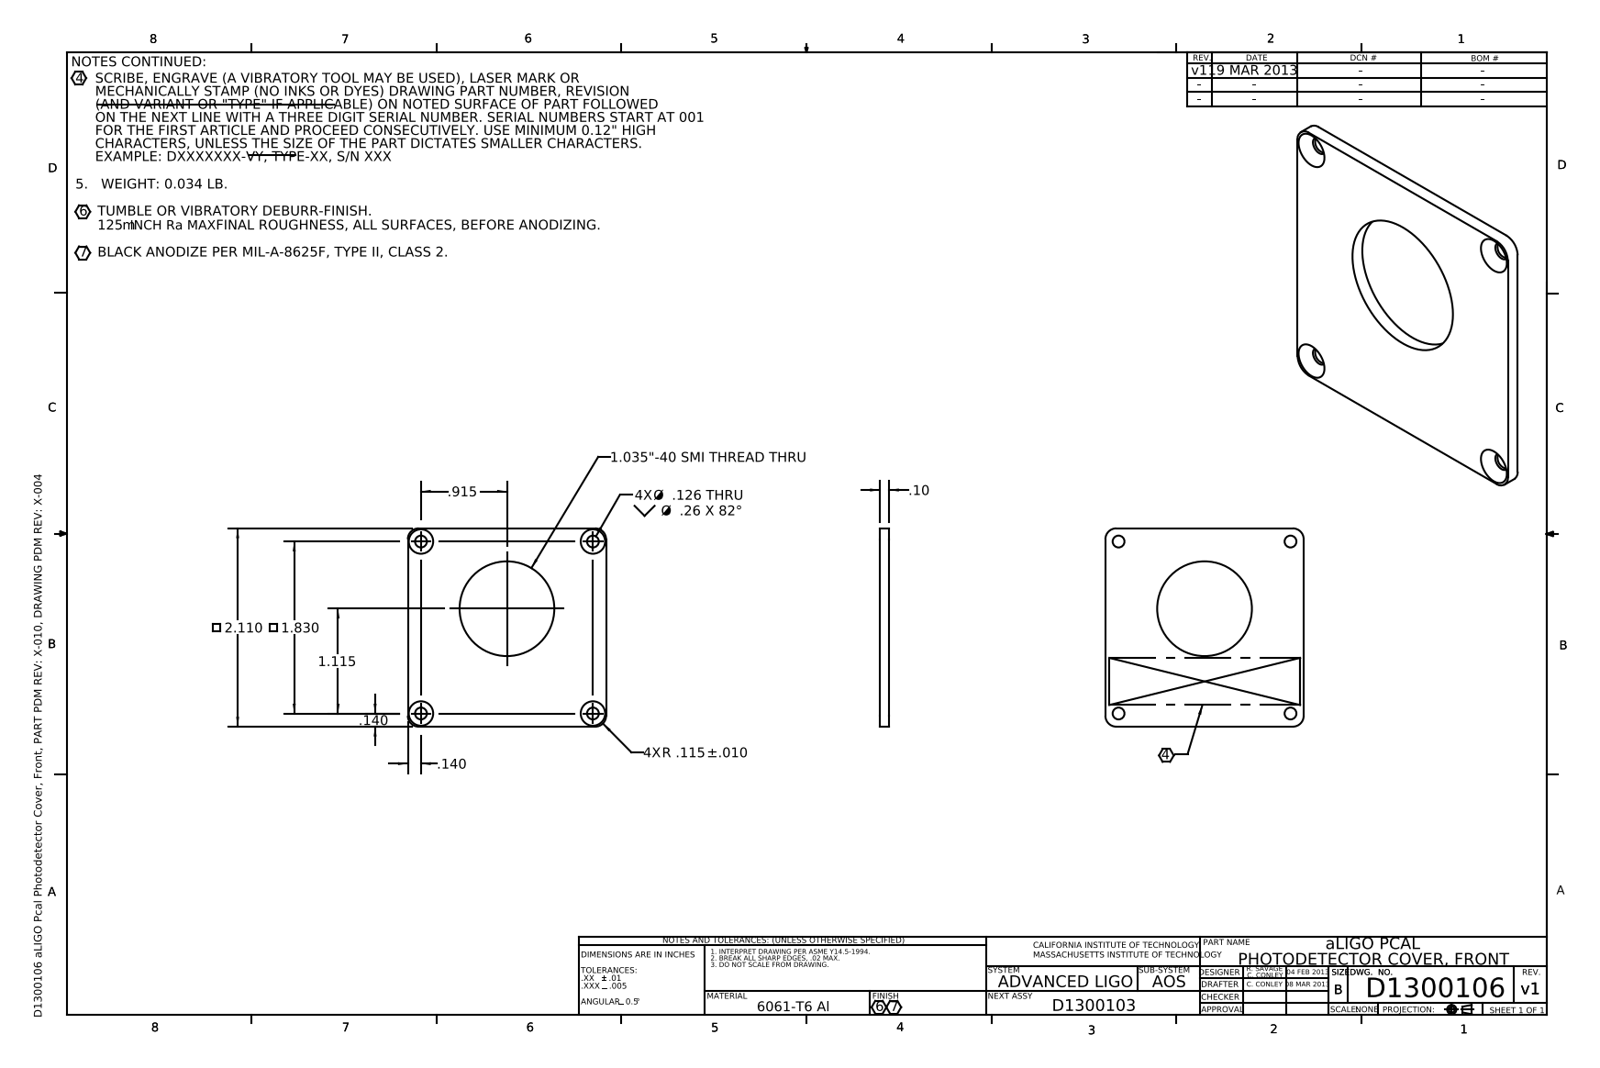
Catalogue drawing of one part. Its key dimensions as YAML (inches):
part_name: "D1300106-v1 aLIGO Pcal Photodetector Cover, Front"
step_written_by: "SolidWorks 2013 (AUTOMOTIVE_DESIGN)"
units: inches
bodies: {solids: 1, faces: 28, planar: 6, cylindrical: 14, other: 8}
overall_size: [2.11, 2.11, 0.098]
volume: 0.348
surface_area: 8.428
round_holes:
  - {diameter: 0.126, count: 4}
  - {diameter: 1.008, count: 1}
partial_cylinders:
  - {radius: 0.115, count: 4}
face_to_face_distances: [0.098, 2.11]
hole_center_spacings: [1.83, 1.161, 1.442, 2.588]
